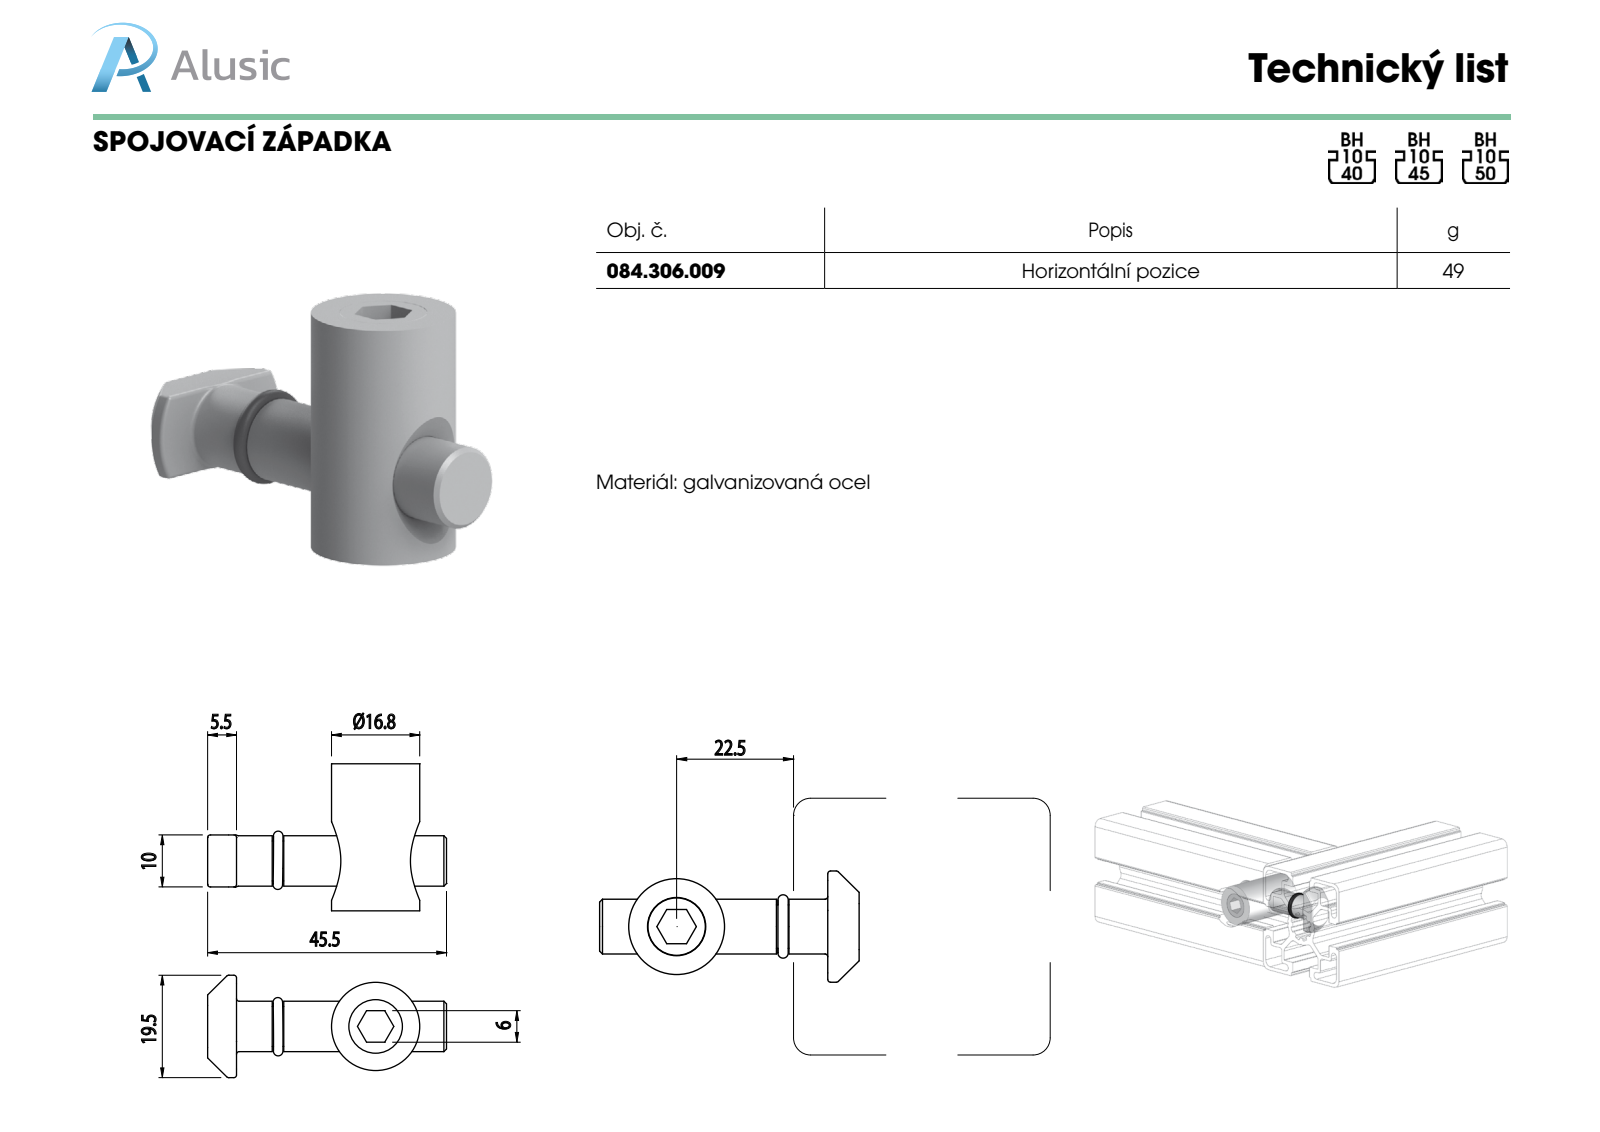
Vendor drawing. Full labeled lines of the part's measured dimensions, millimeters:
Part name (STEP PRODUCT): 084.306.009; o-rings series a_iso_O-ring 7.5x1.8-A-ISO 3601-1; socket set screw cone point_iso_ISO 4027 - M12 x 16-C; 084.306.009B (+1 more)
STEP written by: SolidWorks 2011 (CONFIG_CONTROL_DESIGN)
Units: millimetres
Bodies: 4 solids, 95 faces (18 planar, 29 cylindrical, 48 other)
Overall size (bounding box): 45.5 × 28 × 19.5
Volume: 8 056 mm³ · Surface area: 5 293 mm²
Round holes (diameter × count): ⌀9.7 ×1, ⌀10.2 ×1
Round bosses / shafts (diameter × count): ⌀16.8 ×1, ⌀12 ×1, ⌀9.6 ×1, ⌀7.6 ×1
Partial cylindrical surfaces — rounded edges, fillets, slot ends (radius × count): R0.5 ×8, R9.75 ×1
Main face-to-face distances: 28, 6, 5.5, 14.45, 13.55, 4.55, 9.9, 23.45, 45.5, 40
